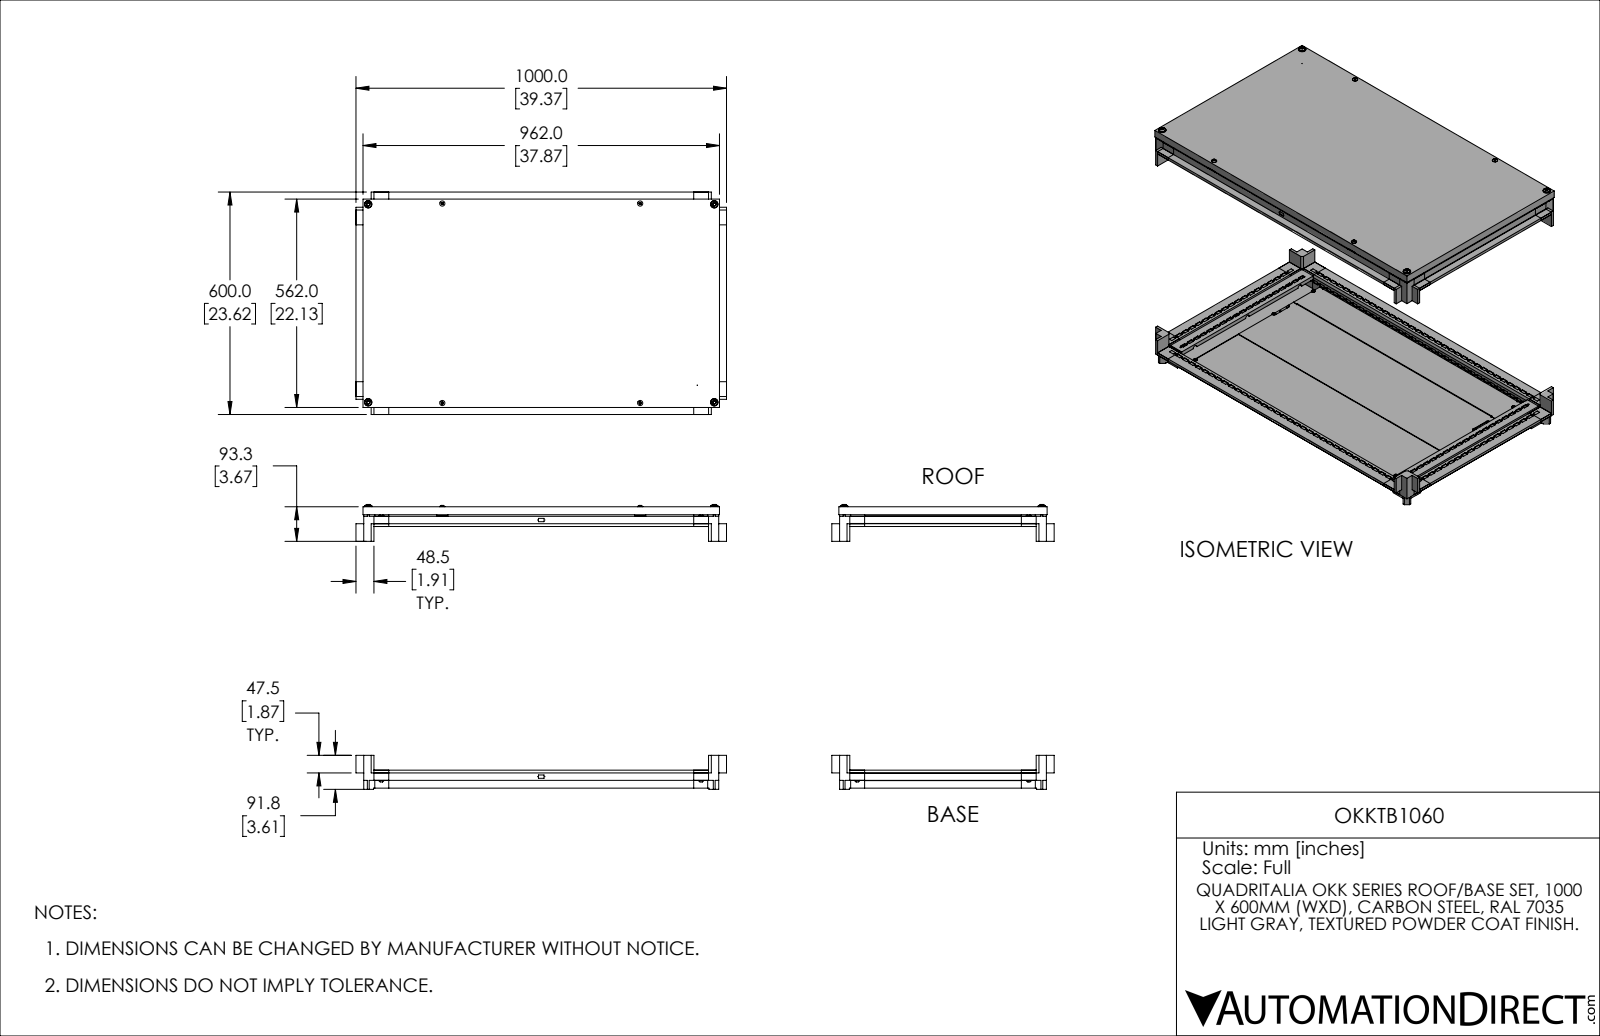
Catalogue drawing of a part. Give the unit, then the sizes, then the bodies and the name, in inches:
Units: inches
Overall size (bounding box): 39.37 × 30.249 × 23.622
Round holes (diameter × count): ⌀0.167 ×268, ⌀0.01 ×12, ⌀0.354 ×7, ⌀0.531 ×4, ⌀0.039 ×1
Round bosses / shafts (diameter × count): ⌀0.787 ×4, ⌀0.551 ×4, ⌀0.472 ×4, ⌀0.236 ×4
Partial cylindrical surfaces — rounded edges, fillets, slot ends (radius × count): R0.02 ×48, R0.084 ×16, R0.03 ×10, R0.138 ×8, R0.217 ×6, R0.276 ×3, R0.089 ×2
Main face-to-face distances: 0.059, 28.95, 29.009, 0.787, 1.083, 28.891, 0.295, 0.098, 1.102, 0.807
Hole centre spacings: 0.984, 1.969, 2.953, 3.937, 4.921, 5.906, 6.89, 7.874
Volume: 525.3 in³ · Surface area: 5 521 in²
Bodies: 2 solids, 3944 faces (3279 planar, 633 cylindrical, 32 other)
Part name (STEP PRODUCT): OKKTB1060
STEP written by: SolidWorks 2021 (AUTOMOTIVE_DESIGN)
